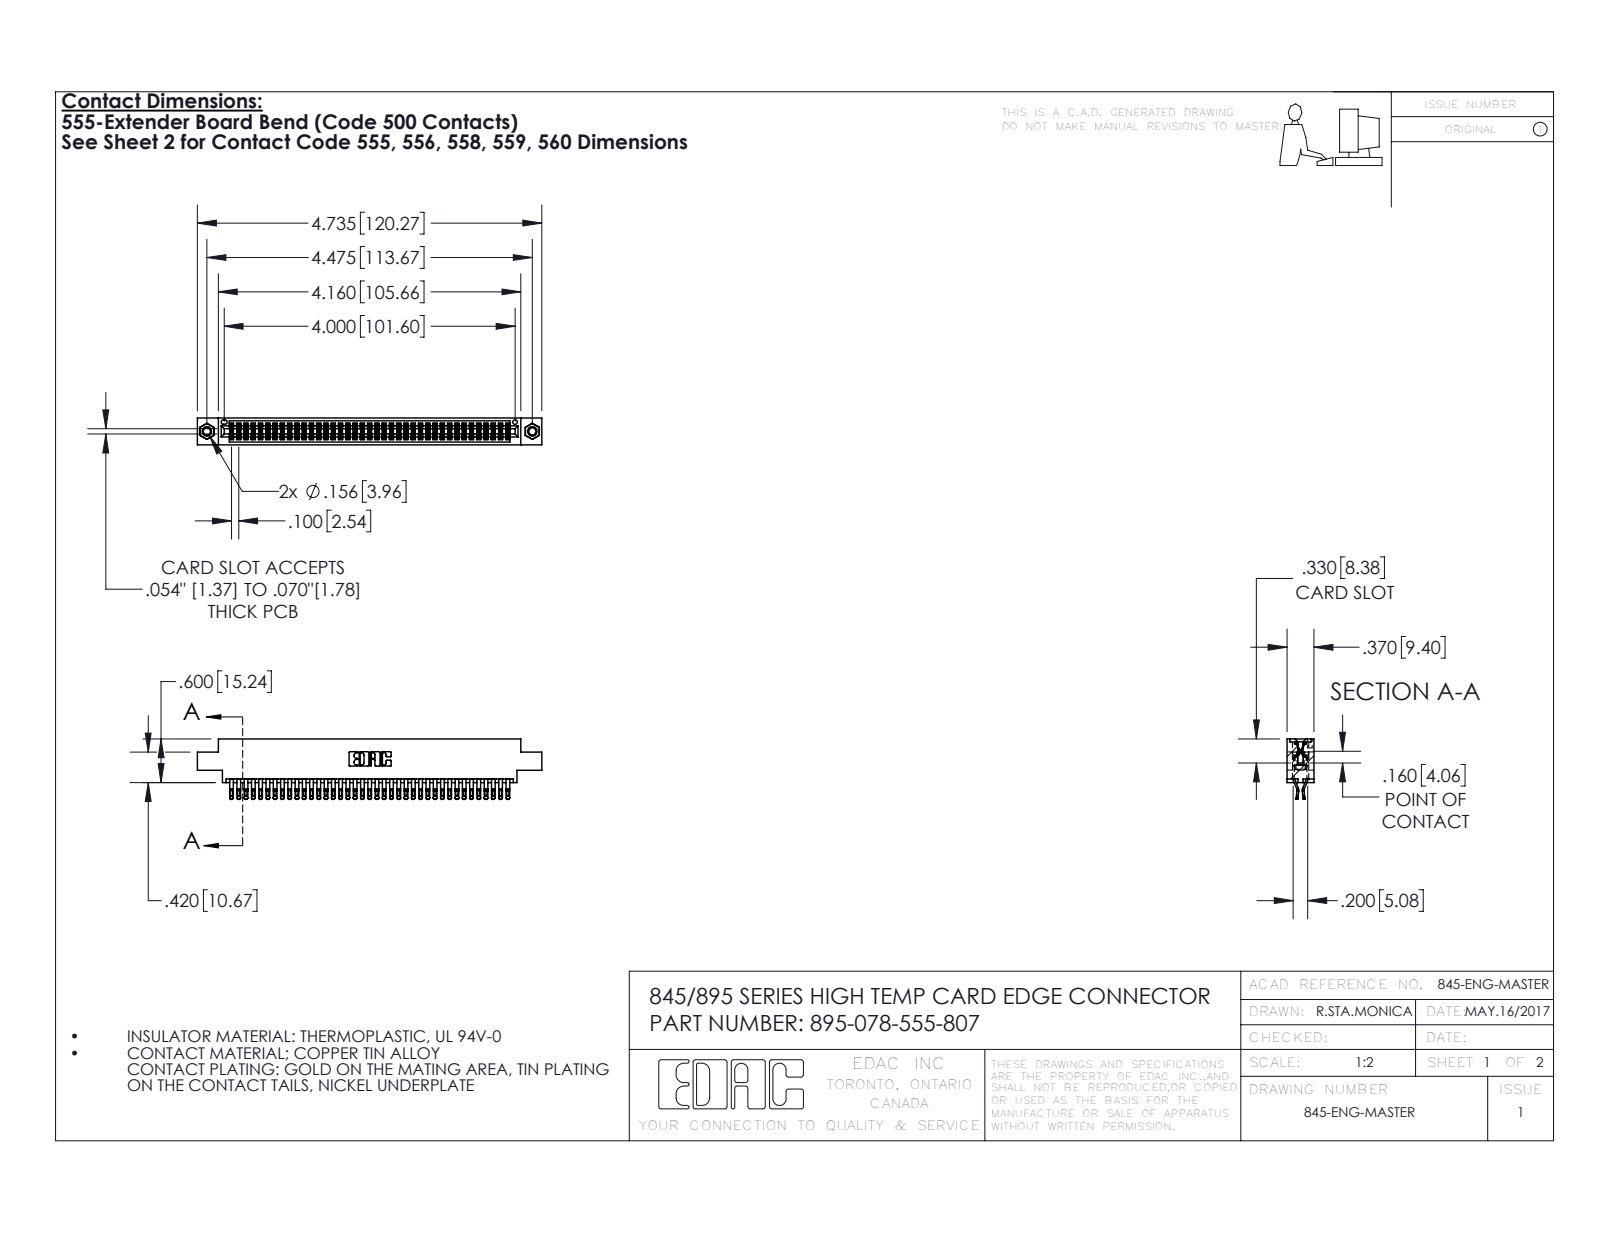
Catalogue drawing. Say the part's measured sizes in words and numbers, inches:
The part is named "345-250-001_345-250-005-103; 395-078-555-807; 345 Part_0.170 Offset - 0.156 Dia-TI; 345-292-001_555 Tail". Its 3-D file was written by "SolidWorks 2016 (CONFIG_CONTROL_DESIGN)". It is 81 solids with 4558 faces: 2534 planar, 2008 cylindrical and 16 other. Overall it measures 4.735 by 0.832 by 0.37 inches. Its volume is 0.717 cubic inches and its surface area 28.33 square inches. Round holes: 2 of diameter 0.098, 2 of diameter 0.125, 2 of diameter 0.156, 1 of diameter 0.064. Round bosses or shafts: 2 of diameter 0.155. Partial cylindrical surfaces (rounded edges, fillets, slot ends): 195 of radius 0.016, 156 of radius 0.02, 117 of radius 0.006, 22 of radius 0.01, 6 of radius 0.007, 6 of radius 0.031, 3 of radius 0.026, 2 of radius 0.01. The main face-to-face distances are 0.072, 0.298, 0.37, 0.025, 0.2, 0.098, 0.272, 0.225, 0.175, 0.149. The hole center spacings are 0.27, 4.239, 4.475.
